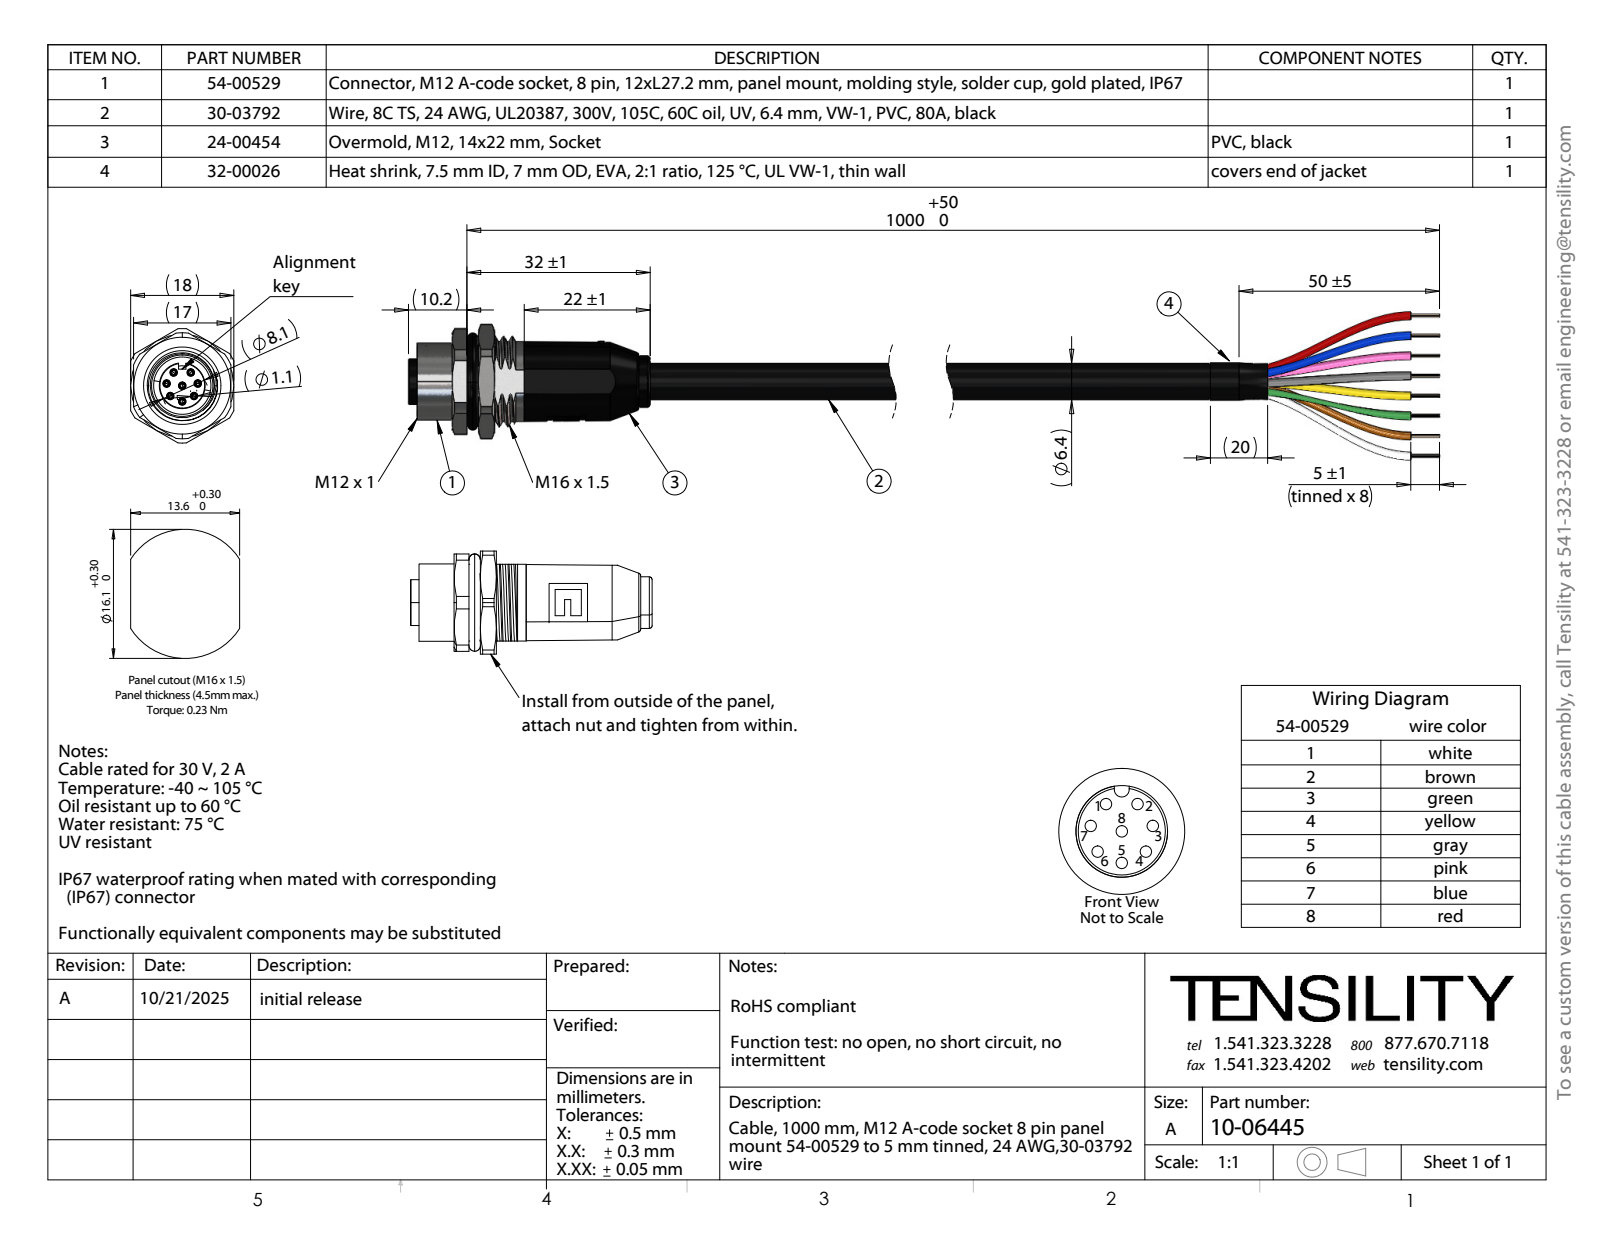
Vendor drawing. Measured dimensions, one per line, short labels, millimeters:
name: 10-06445; 54-00529; 30-03792_50mm; 32-00026_10 mm (+2 more)
written by: SolidWorks 2025 (CONFIG_CONTROL_DESIGN)
unit: mm
bodies: 336 solids, 2190 faces (893 planar, 967 cylindrical, 330 other)
size: 227.2 × 25.9 × 18
volume: 11 135 mm³; area: 12 480 mm²
holes: 8× ⌀1.2, 8× ⌀1.3, 8× ⌀1.6, 1× ⌀7.5, 1× ⌀8.8, 1× ⌀9.1, 1× ⌀9.6, 1× ⌀11.2, 1× ⌀12.2, 1× ⌀14.7
bosses: 8× ⌀1.7, 8× ⌀1.56, 8× ⌀1.52, 1× ⌀13.95, 1× ⌀13.5, 1× ⌀12.5, 1× ⌀11, 1× ⌀10.7
rounds: 8× R0.5, 1× R7.04, 1× R7.9, 1× R9.25, 1× R10
face distances: 0.5, 2, 10, 1.5, 2.6, 11.5, 18, 9.5, 8, 17.5
hole spacings: 2.75, 4.15, 2.27, 2.28, 2.29, 4.64, 5.27, 5.28
